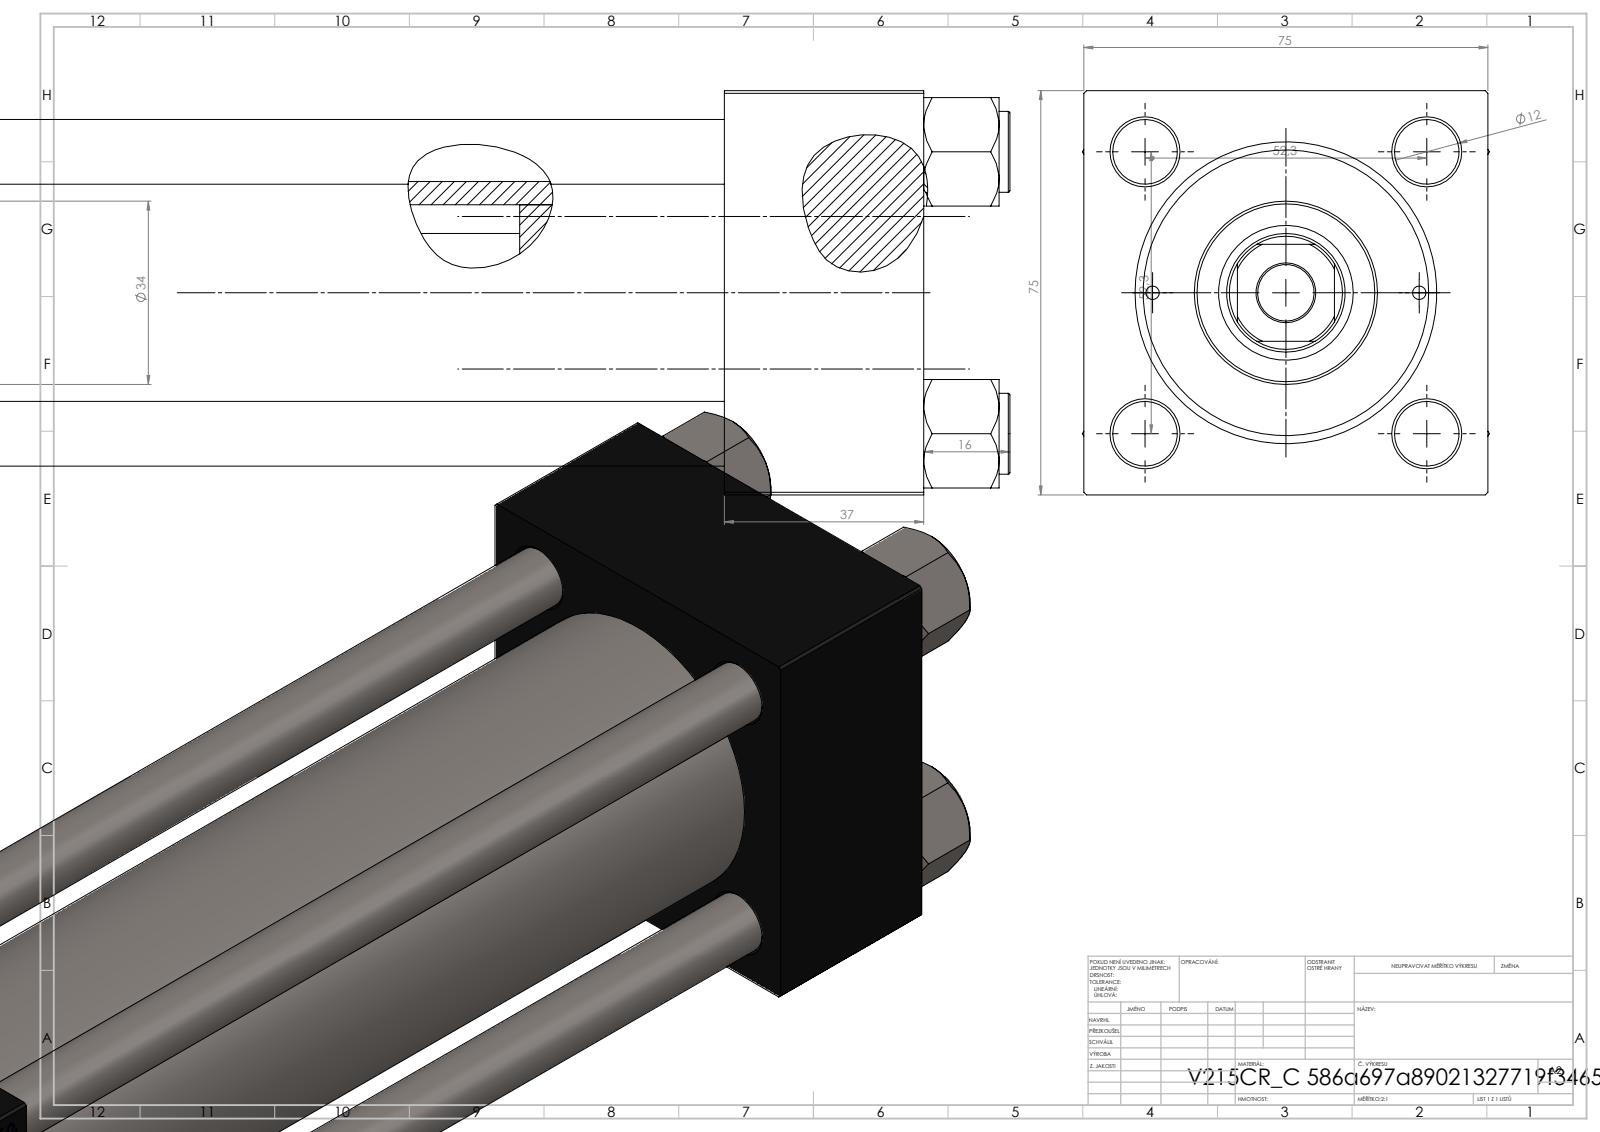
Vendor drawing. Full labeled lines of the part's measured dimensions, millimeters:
Part name (STEP PRODUCT): V215_VC_A; V215CR_C_Body; V215CR_VCP_C; NUT_M5_C (+1 more)
STEP written by: SolidWorks 2019 (CONFIG_CONTROL_DESIGN)
Units: millimetres
Bodies: 11 solids, 1154 faces (528 planar, 90 cylindrical, 536 other)
Overall size (bounding box): 335 × 75.54 × 75
Volume: 843 400 mm³ · Surface area: 224 773 mm²
Round holes (diameter × count): ⌀12 ×4, ⌀2.5 ×2, ⌀7 ×2, ⌀20.96 ×2, ⌀30 ×2, ⌀10.5 ×1, ⌀22 ×1, ⌀25 ×1, ⌀41 ×1, ⌀50 ×1, ⌀53 ×1
Round bosses / shafts (diameter × count): ⌀15 ×4, ⌀56 ×1, ⌀34 ×1
Partial cylindrical surfaces — rounded edges, fillets, slot ends (radius × count): R10.5 ×1
Main face-to-face distances: 75, 37, 294, 257, 235, 198, 59, 265.3, 228.3, 30.3
Hole centre spacings: 26.19, 36.98, 52.3, 57.22, 24.75, 73.96, 49.5, 233.5
